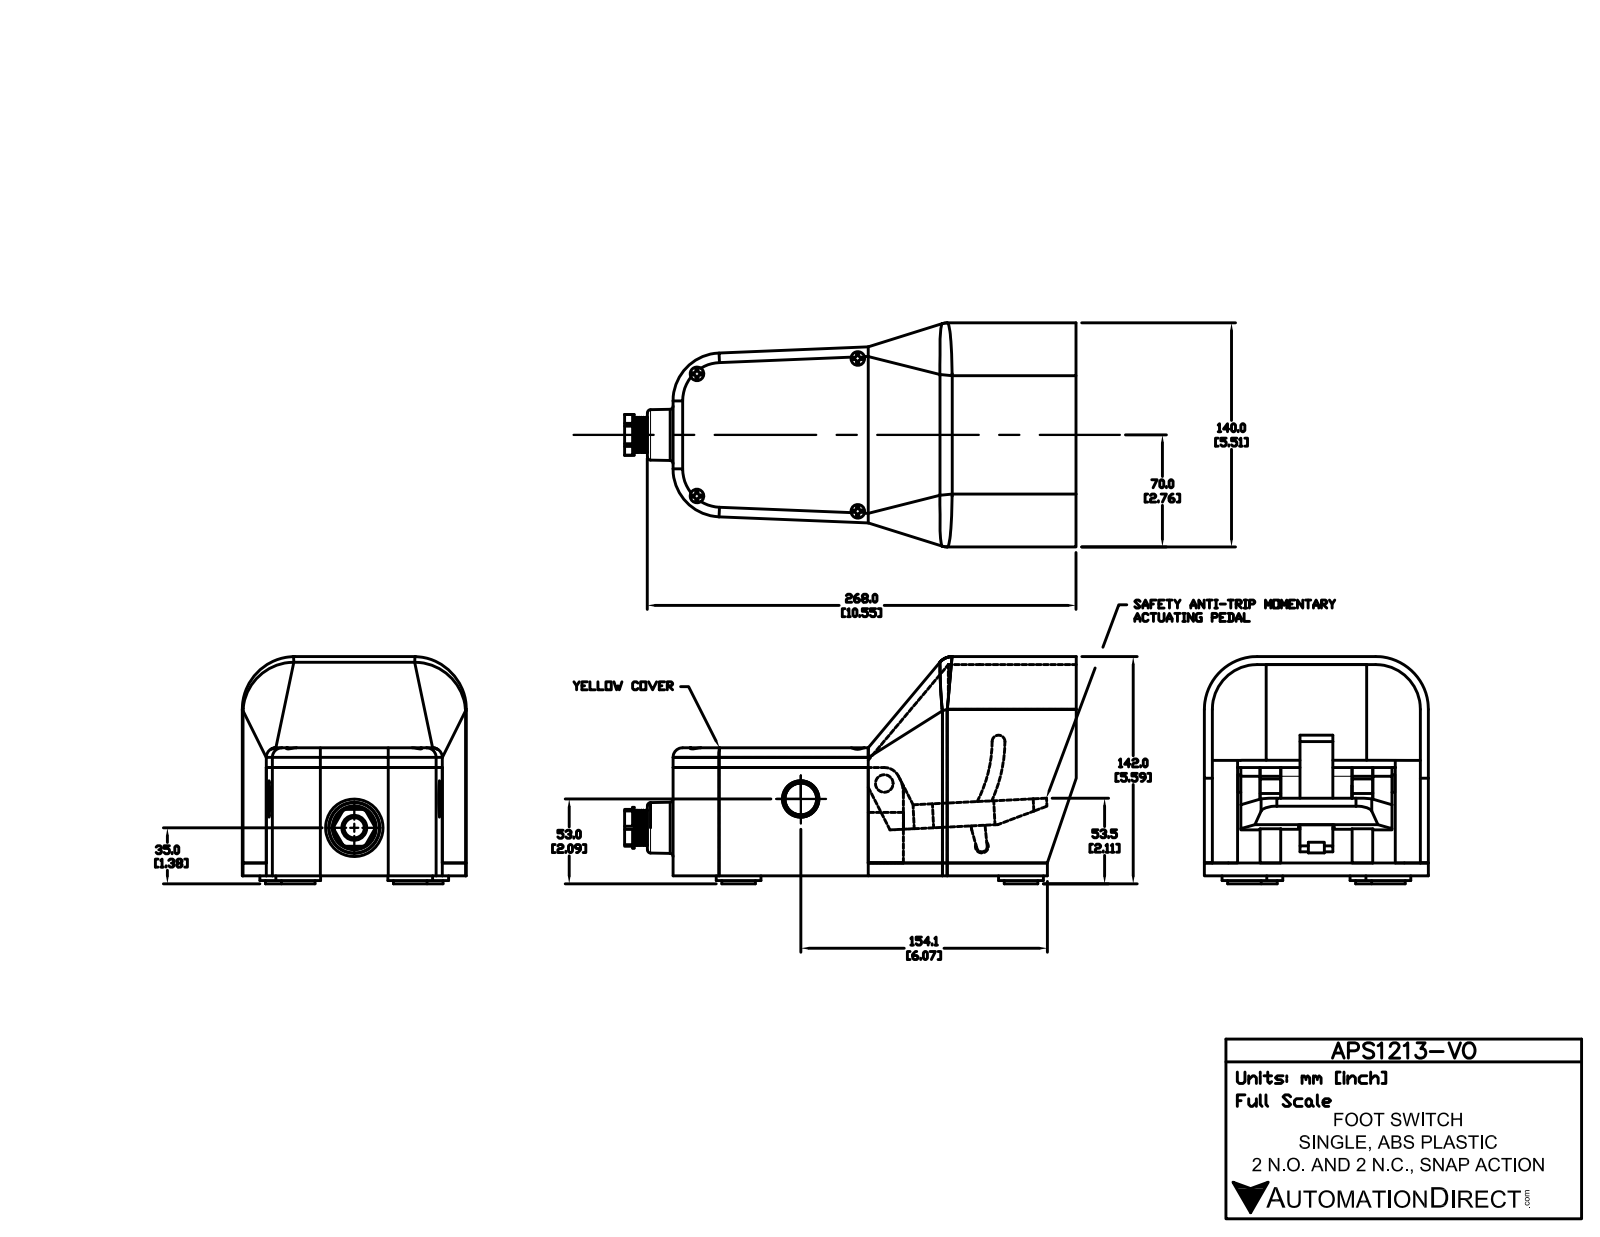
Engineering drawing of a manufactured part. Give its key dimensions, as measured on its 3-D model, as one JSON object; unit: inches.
{"part_name": "APS1211-V0", "step_written_by": "SolidWorks 2015 (AUTOMOTIVE_DESIGN)", "units": "inches", "bodies": {"solids": 19, "faces": 379, "planar": 220, "cylindrical": 103, "other": 56}, "overall_size": [11.112, 5.591, 5.512], "volume_in3": 94.77, "surface_area_in2": 422.3, "round_holes": [[0.335, 4], [0.896, 2], [0.498, 1], [0.614, 1]], "round_bosses_or_shafts": [[1.102, 4], [0.827, 4], [0.782, 2], [1.004, 1], [0.866, 1], [0.433, 1]], "partial_cylinders_radius": [[0.039, 16], [0.394, 7], [0.236, 3], [0.787, 2], [1.102, 2], [1.181, 2], [1.299, 2], [0.132, 1]], "face_to_face_distances": [0.197, 5.315, 0.315, 2.348, 2.664, 2.349, 2.663, 5.512, 3.15, 2.835], "hole_center_spacings": [3.976, 5.206, 3.004, 3.76]}
